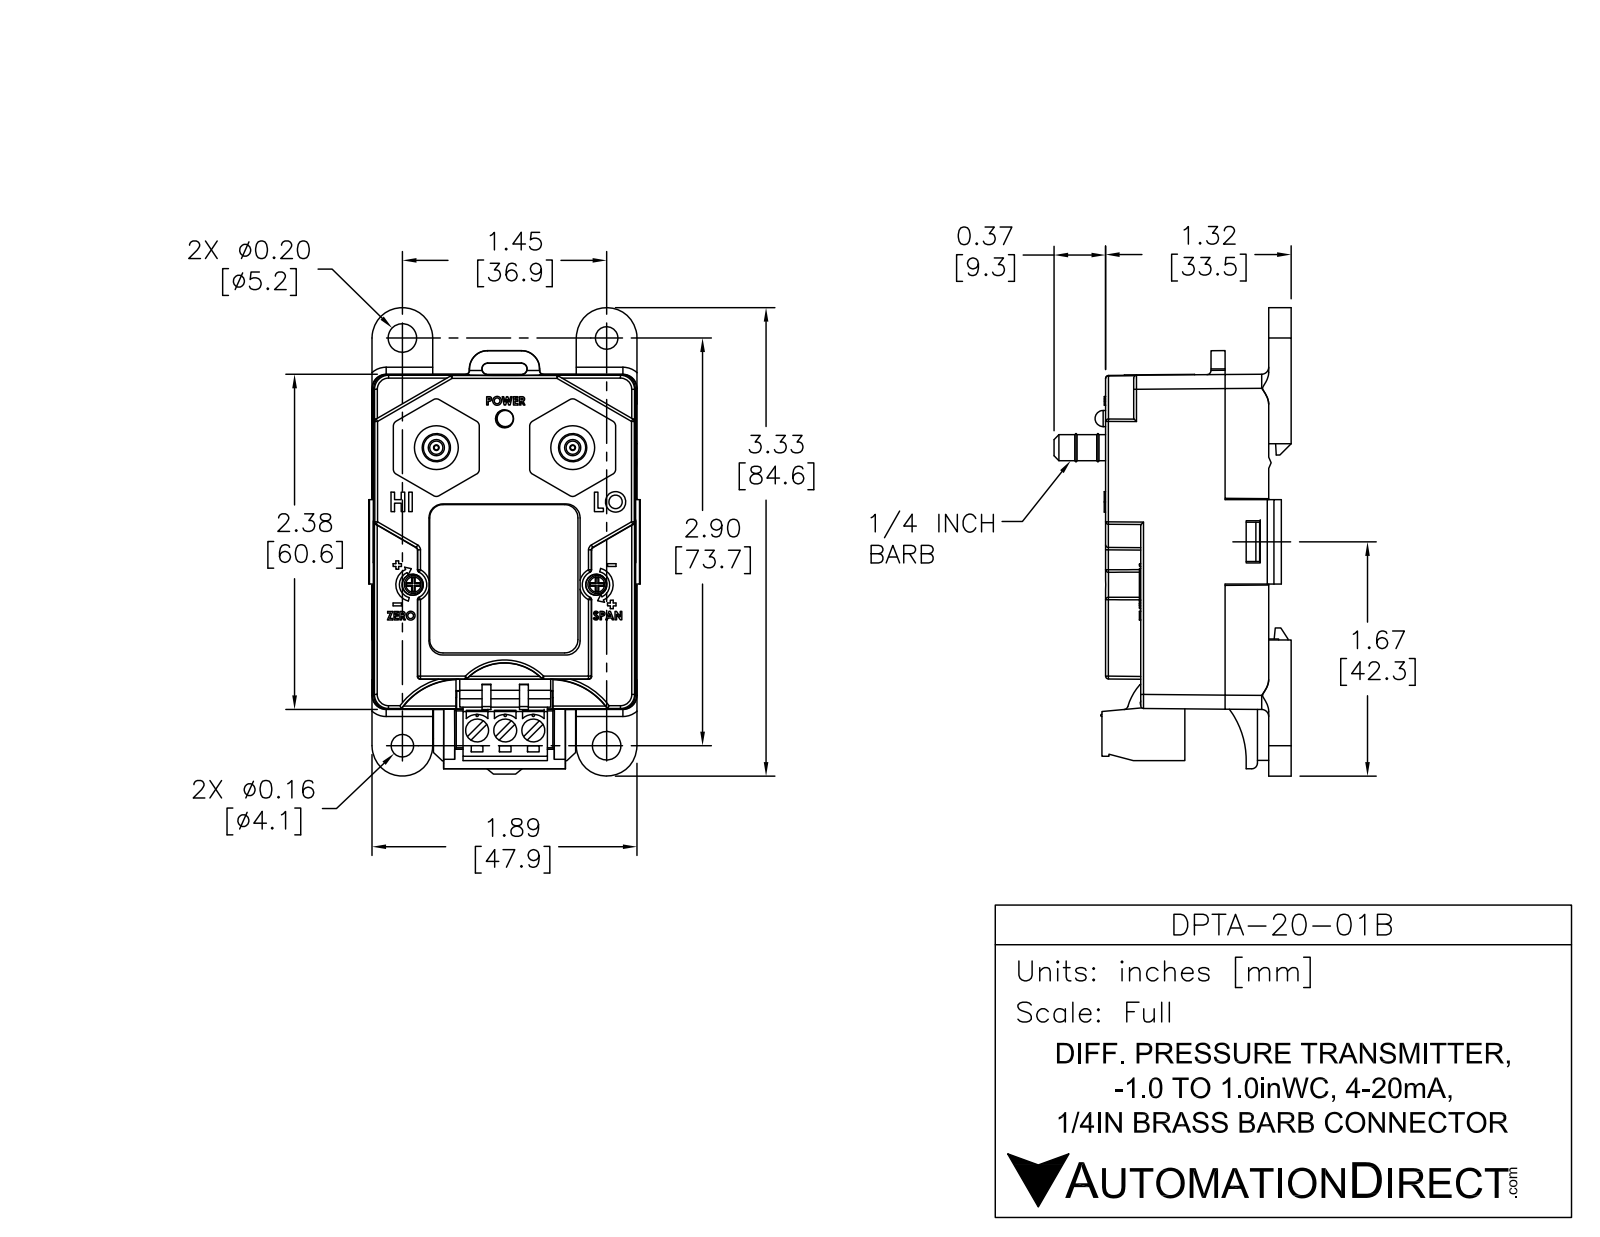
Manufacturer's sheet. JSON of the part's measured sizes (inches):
{"part_name": "DPTA-20-01B", "step_written_by": "SolidWorks 2011 (AUTOMOTIVE_DESIGN)", "units": "inches", "bodies": {"solids": 11, "faces": 448, "planar": 354, "cylindrical": 85, "other": 9}, "overall_size": [3.347, 1.959, 1.697], "volume_in3": 1.811, "surface_area_in2": 53.85, "round_holes": [[0.157, 7], [0.098, 2], [0.202, 2], [0.122, 1]], "round_bosses_or_shafts": [[0.197, 3], [0.138, 3], [0.138, 3], [0.315, 2], [0.187, 2], [0.118, 1]], "partial_cylinders_radius": [[0.118, 12], [0.079, 4], [0.217, 4], [0.039, 2], [0.042, 2], [0.044, 2], [0.094, 2], [0.128, 2]], "face_to_face_distances": [0.039, 0.075, 0.157, 1.146, 0.02, 1.846, 0.232, 0.197, 1.303, 1.071], "hole_center_spacings": [0.533, 0.816, 0.92, 0.981, 1.159, 1.357, 1.444, 1.505]}
